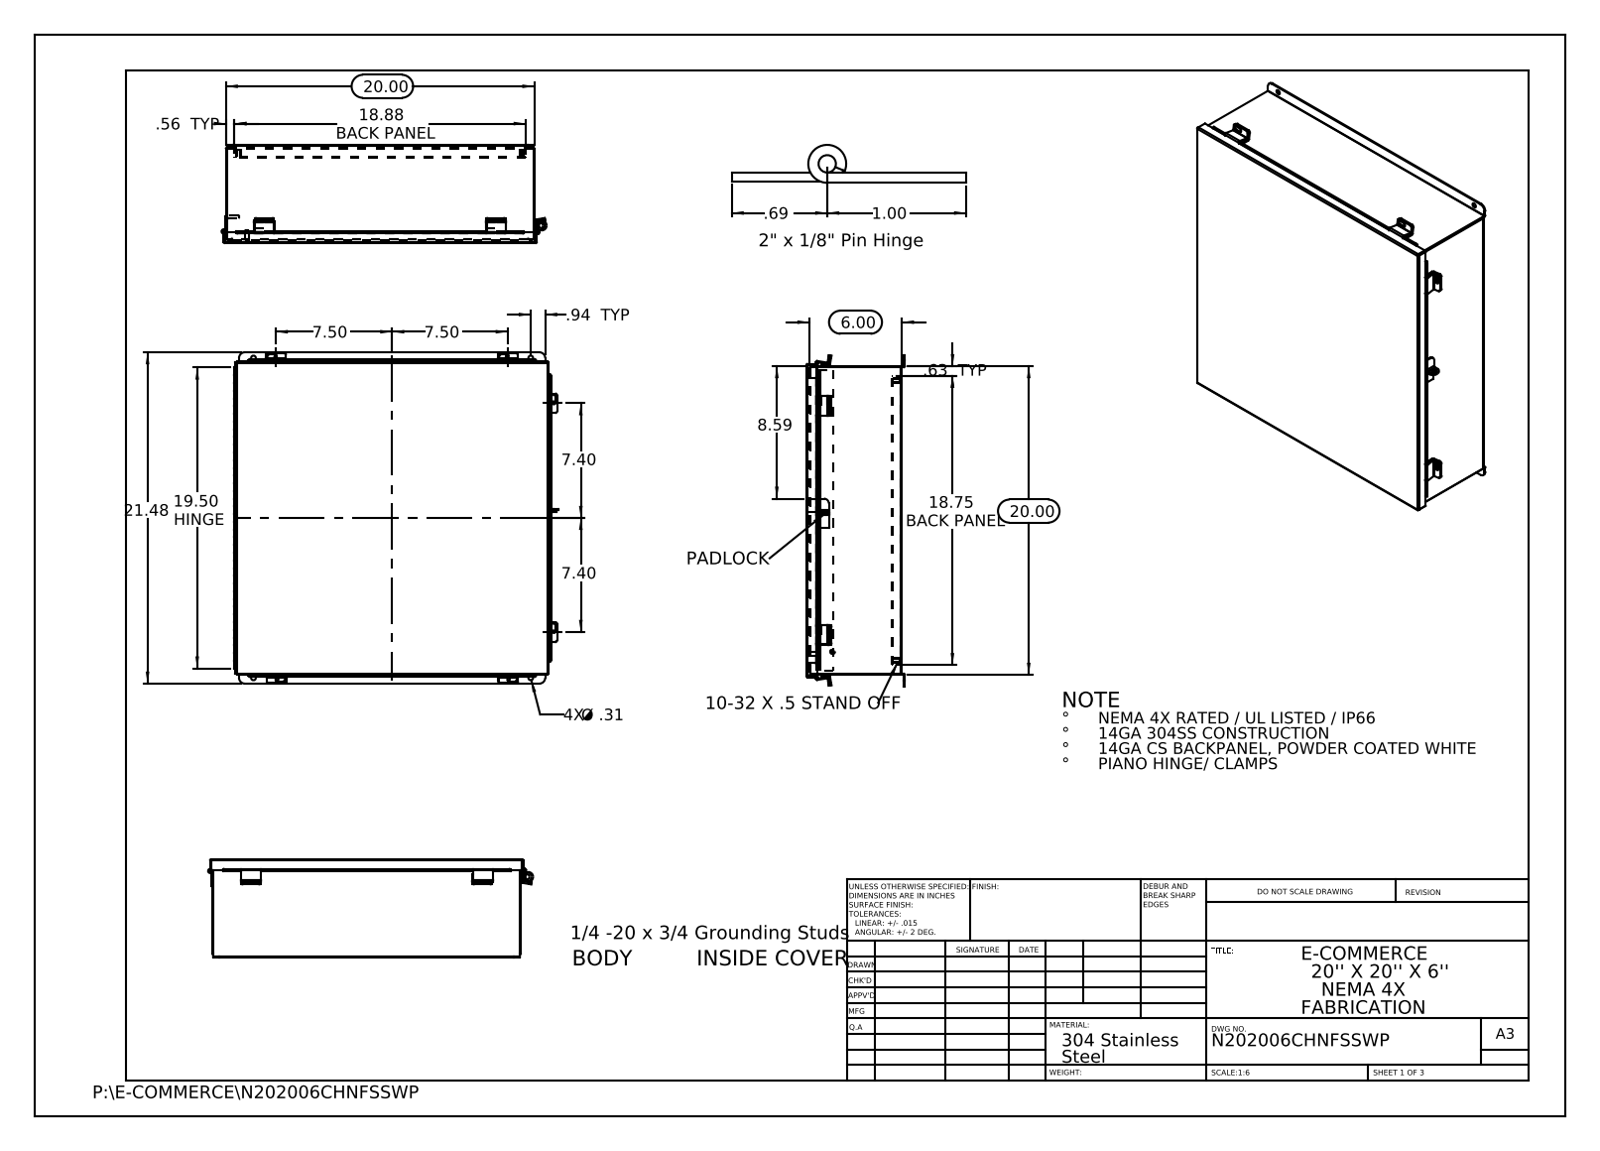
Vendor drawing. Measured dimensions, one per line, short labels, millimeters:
name: N202006CHNFSSWP JIC Bottom; N202006CHNFSSWP JIC_Standoff; HW-CLH-JH-20104; N202006CHNFSSWP Hinge Cover Side JIC (+8 more)
written by: SolidWorks 2013 (CONFIG_CONTROL_DESIGN)
unit: mm
bodies: 27 solids, 938 faces (579 planar, 339 cylindrical, 20 other)
size: 545.5 × 535.2 × 162.3
volume: 2 217 000 mm³; area: 2 367 000 mm²
holes: 10× ⌀6.4, 4× ⌀4.7, 4× ⌀7.9, 1× ⌀3.2, 1× ⌀3.2, 1× ⌀9.5, 1× ⌀9.5
bosses: 4× ⌀8, 2× ⌀8, 2× ⌀6, 1× ⌀6.9, 1× ⌀6.4
rounds: 21× R3.2, 13× R0.3, 12× R0.2, 12× R2.2, 12× R3.4, 6× R2.1, 6× R2.5, 4× R9.5
face distances: 1.9, 155.7, 506.1, 153.7, 157.6, 1.9, 143, 14.6, 12.7, 141
hole spacings: 33.4, 462.8, 493.4, 675.7, 381, 456.6, 460.4, 466.7
